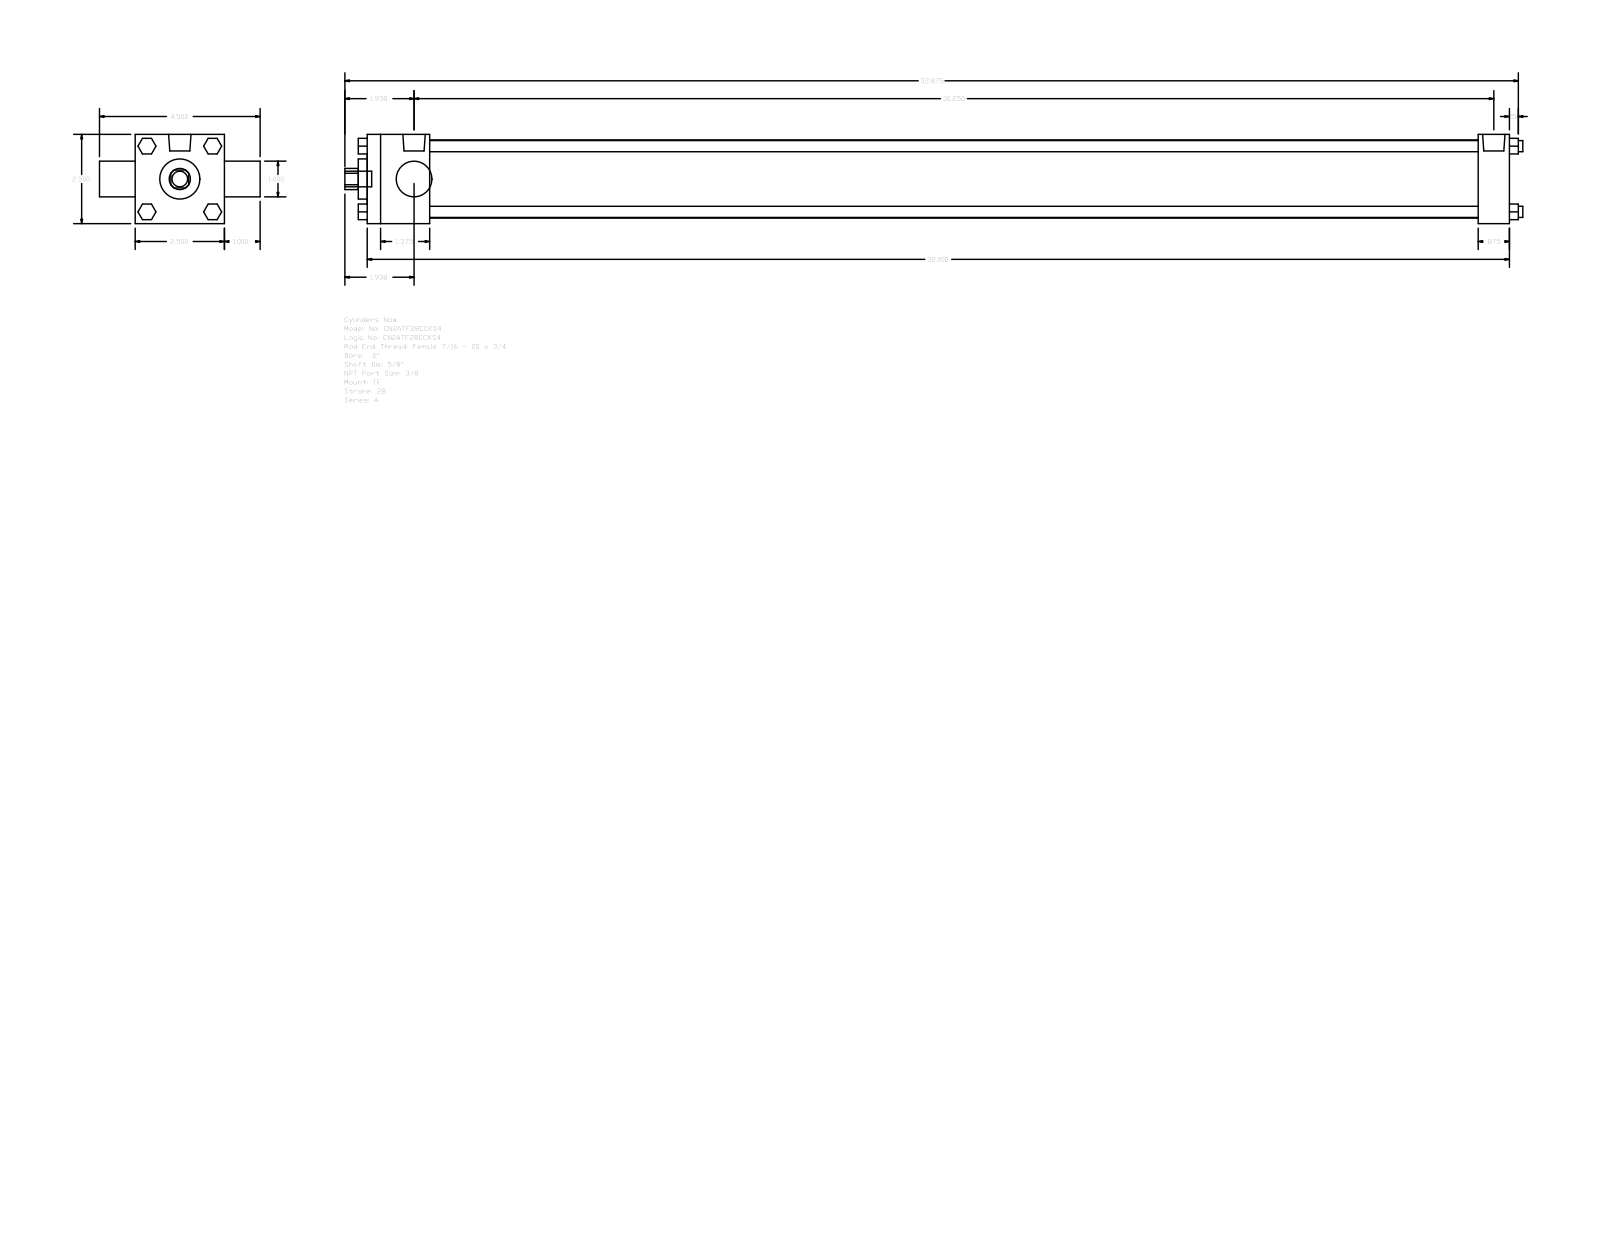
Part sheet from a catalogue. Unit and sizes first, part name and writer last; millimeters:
Units: millimetres
Overall size (bounding box): 838.2 × 114.3 × 63.5
Round holes (diameter × count): ⌀15.88 ×1, ⌀25.4 ×1, ⌀28.57 ×1, ⌀55.63 ×1
Round bosses / shafts (diameter × count): ⌀7.94 ×4, ⌀5.56 ×3, ⌀15.93 ×2, ⌀11.11 ×1
Partial cylindrical surfaces — rounded edges, fillets, slot ends (radius × count): R7.54 ×1
Main face-to-face distances: 63.5, 812.79, 44.45, 790.57, 746.12, 768.34, 22.22, 25.4, 88.9, 6.35
Bodies: 0 solids, 120 faces (92 planar, 28 cylindrical, 0 other)
Part name (STEP PRODUCT): A_TF__0200_0.625
STEP written by: GSSL Pune (CONFIG_CONTROL_DESIGN)
